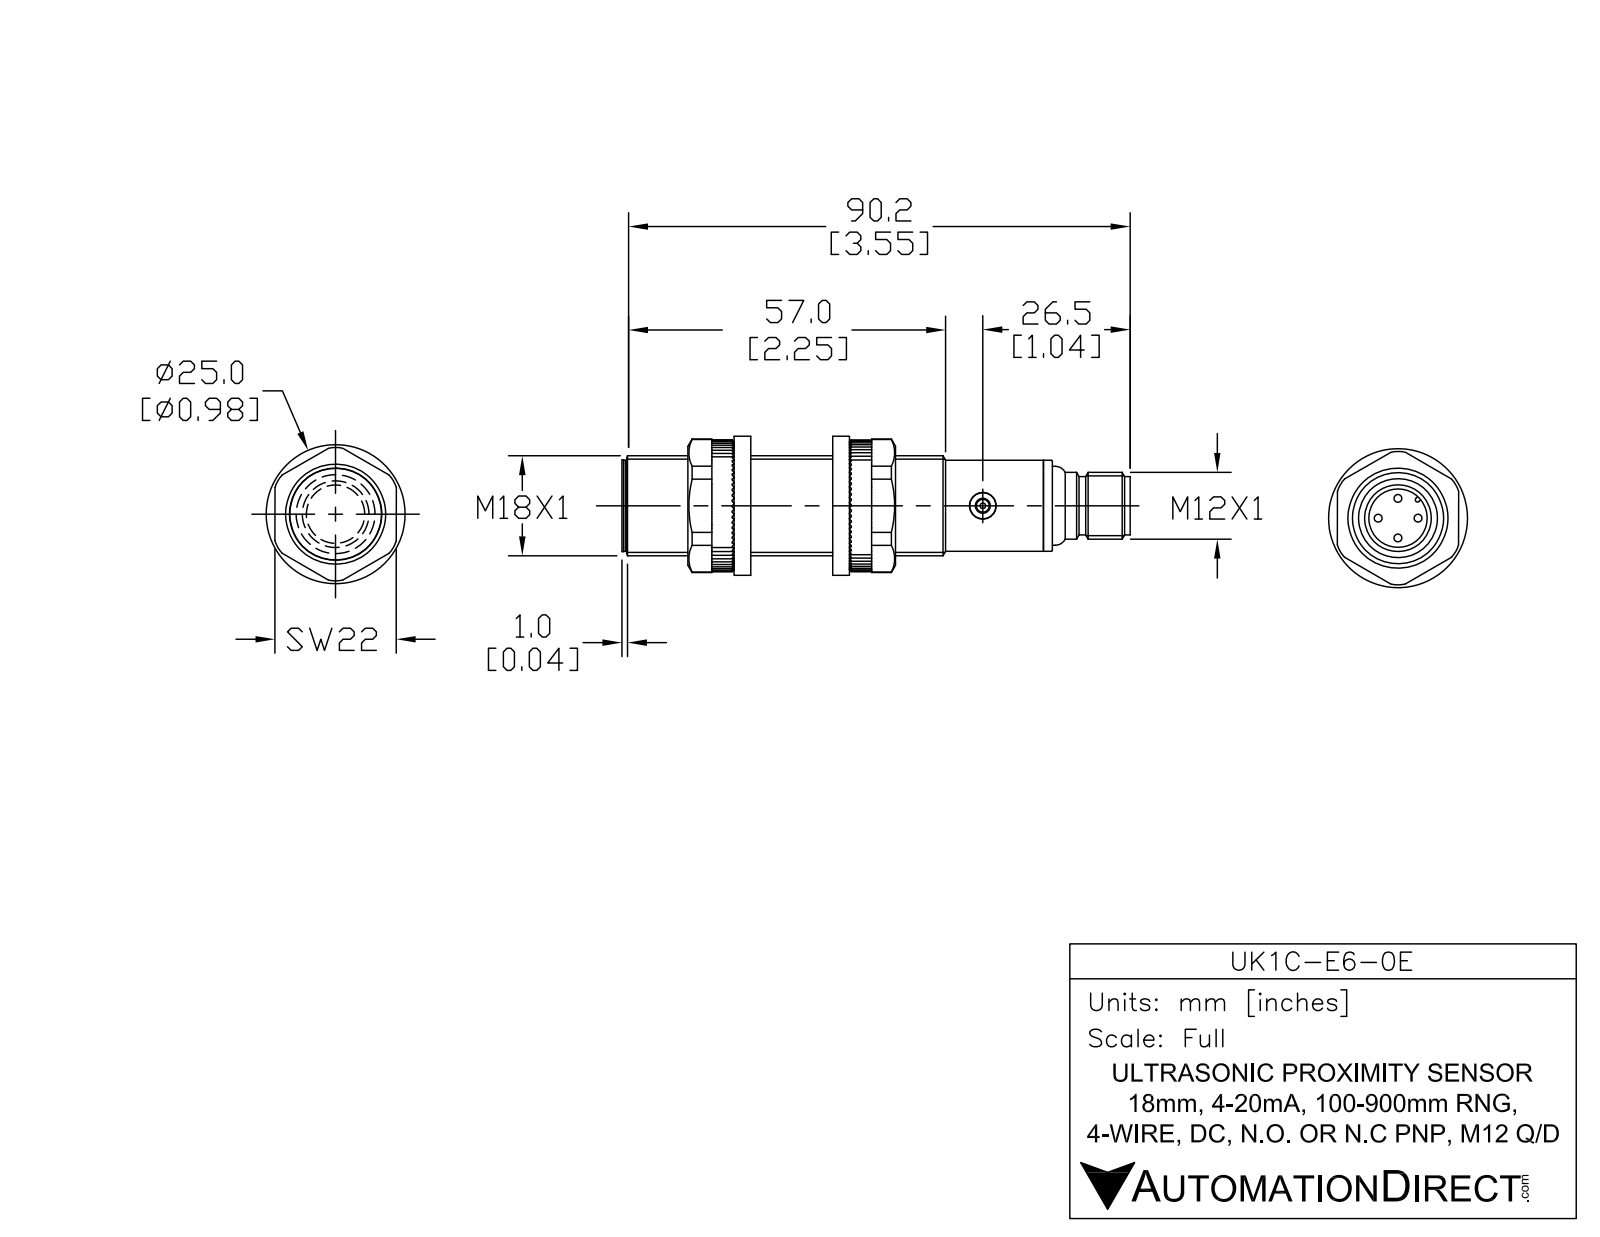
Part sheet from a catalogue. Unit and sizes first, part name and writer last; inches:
Units: inches
Overall size (bounding box): 3.606 × 0.709 × 0.709
Round holes (diameter × count): ⌀0.106 ×1, ⌀0.185 ×1, ⌀0.276 ×1, ⌀0.327 ×1, ⌀0.374 ×1
Round bosses / shafts (diameter × count): ⌀0.039 ×4, ⌀0.709 ×1, ⌀0.654 ×1, ⌀0.646 ×1, ⌀0.622 ×1, ⌀0.559 ×1, ⌀0.472 ×1, ⌀0.413 ×1
Partial cylindrical surfaces — rounded edges, fillets, slot ends (radius × count): R0.024 ×1
Main face-to-face distances: 2.957, 0.039, 2.996, 0.037, 2.994, 0.043, 0.157, 3.055, 3.053, 3.016
Volume: 1.202 in³ · Surface area: 10.68 in²
Bodies: 6 solids, 106 faces (21 planar, 48 cylindrical, 37 other)
Part name (STEP PRODUCT): UK1C-E6-0E
STEP written by: SolidWorks 2017 (AUTOMOTIVE_DESIGN)
